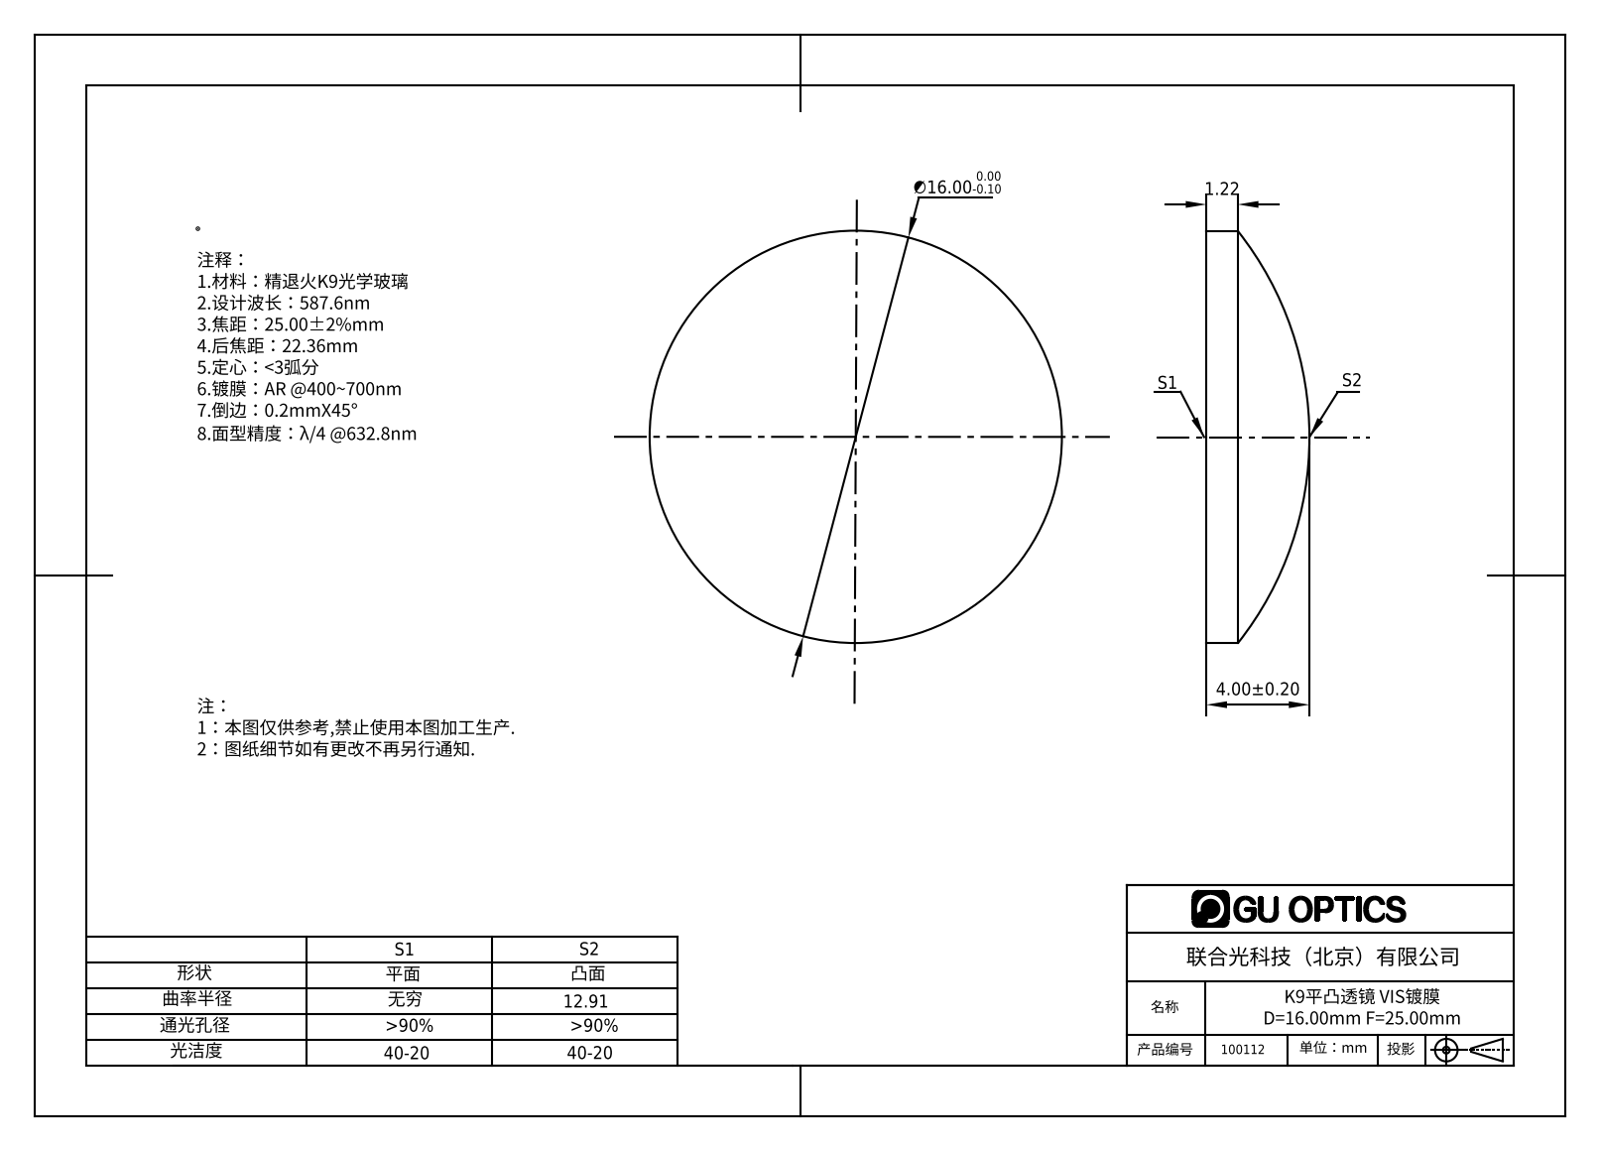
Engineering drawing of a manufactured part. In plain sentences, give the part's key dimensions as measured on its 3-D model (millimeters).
The part is named "100112". Its 3-D file was written by "SolidWorks 2016 (AUTOMOTIVE_DESIGN)". It is 1 solid with 5 faces: 1 planar, 2 cylindrical and 2 other. Overall it measures 16 by 16 by 4 millimeters. Its volume is 536 cubic millimeters and its surface area 488 square millimeters. Round bosses or shafts: 1 of diameter 16.
